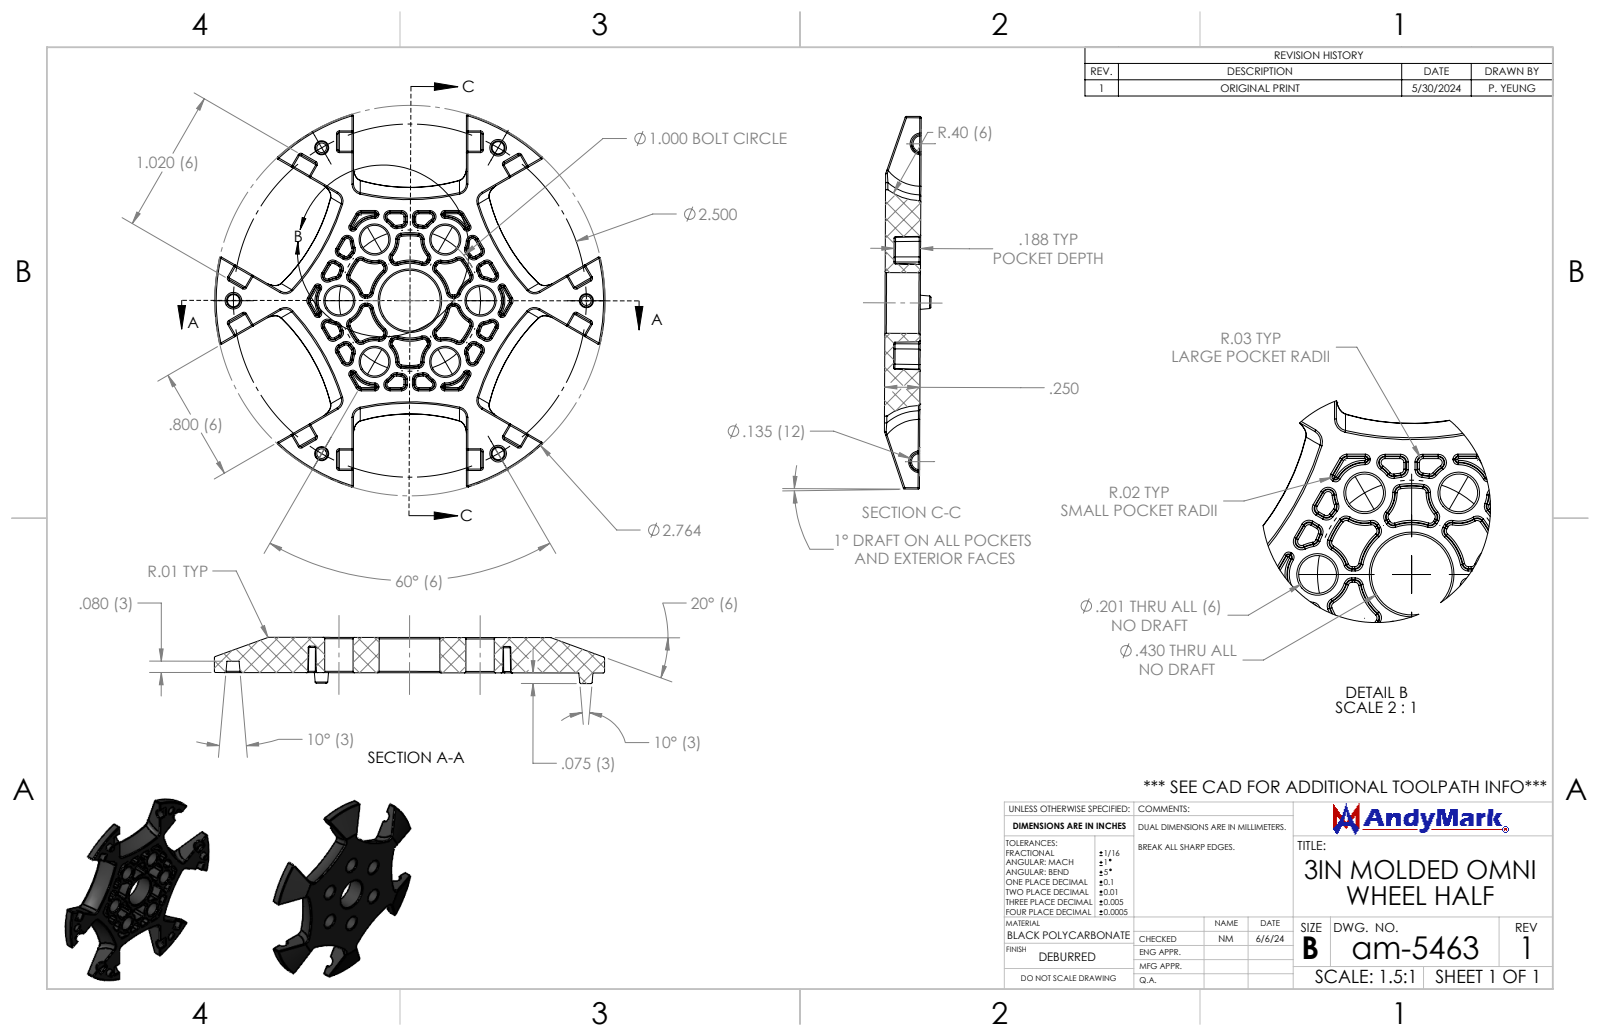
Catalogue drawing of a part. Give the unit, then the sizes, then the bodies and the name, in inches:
Units: inches
Overall size (bounding box): 2.764 × 2.639 × 0.325
Round holes (diameter × count): ⌀0.201 ×6, ⌀0.43 ×1
Partial cylindrical surfaces — rounded edges, fillets, slot ends (radius × count): R0.01 ×88, R0.031 ×18, R0.016 ×12, R0.067 ×5, R0.068 ×1, R1.382 ×1
Main face-to-face distances: 0.25, 0.8, 0.187, 0.063, 0.11, 0.91, 0.656, 1.02, 0.08, 0.107
Hole centre spacings: 0.5, 0.866, 1
Volume: 0.532 in³ · Surface area: 12.3 in²
Bodies: 1 solid, 1145 faces (116 planar, 257 cylindrical, 772 other)
Part name (STEP PRODUCT): am-5463 3IN Molded Omni Wheel Half
STEP written by: SolidWorks 2024 (AUTOMOTIVE_DESIGN)
